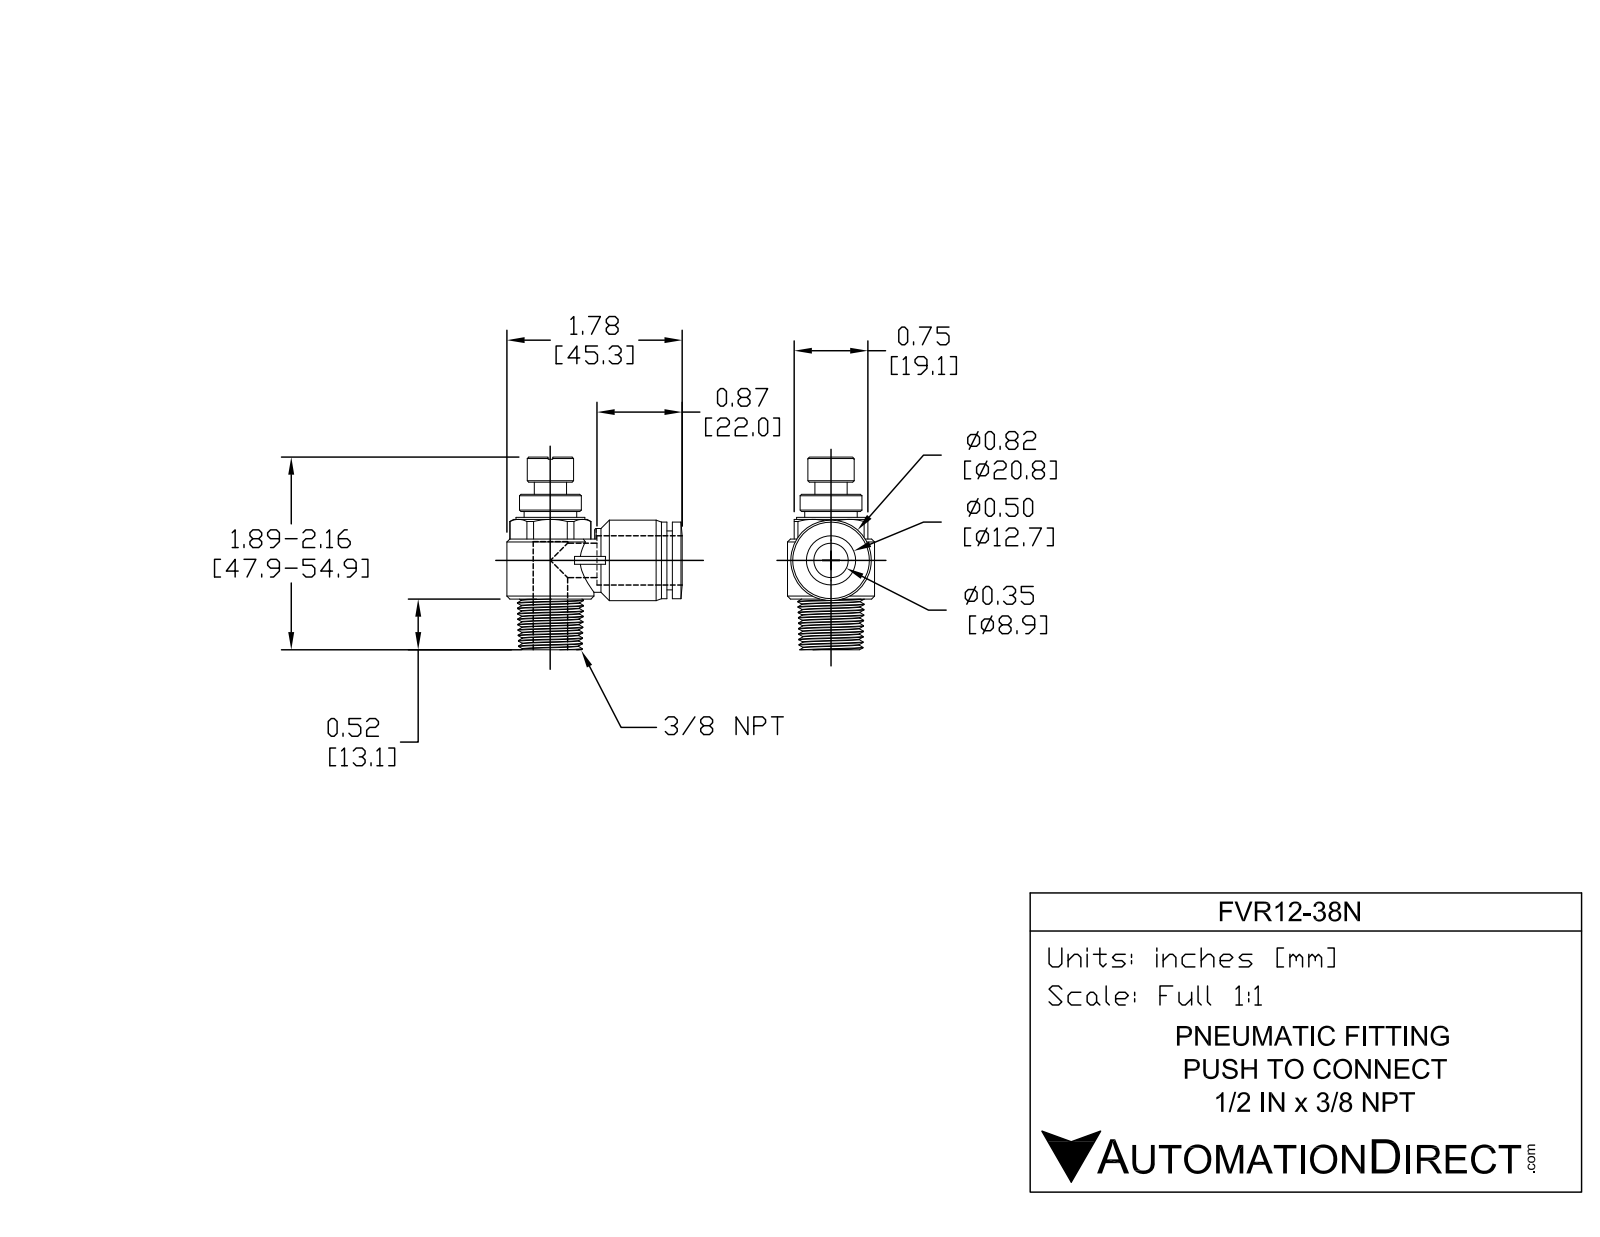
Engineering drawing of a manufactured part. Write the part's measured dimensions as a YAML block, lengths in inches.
part_name: "FVR12-38N"
step_written_by: "SolidWorks 2015 (AUTOMOTIVE_DESIGN)"
units: inches
bodies: {solids: 1, faces: 561, planar: 253, cylindrical: 144, other: 164}
overall_size: [2.161, 1.78, 0.886]
volume: 0.978
surface_area: 11.43
round_holes:
  - {diameter: 0.236, count: 2}
  - {diameter: 0.51, count: 1}
round_bosses_or_shafts:
  - {diameter: 0.886, count: 1}
  - {diameter: 0.819, count: 1}
  - {diameter: 0.787, count: 1}
  - {diameter: 0.783, count: 1}
  - {diameter: 0.748, count: 1}
  - {diameter: 0.677, count: 1}
  - {diameter: 0.65, count: 1}
  - {diameter: 0.591, count: 1}
partial_cylinders:
  - {radius: 0.236, count: 1}
  - {radius: 0.315, count: 1}
  - {radius: 0.413, count: 1}
face_to_face_distances: [0.051, 0.748, 0.555, 1.165, 0.228, 0.811, 1.039, 0.754, 0.805, 0.996]
